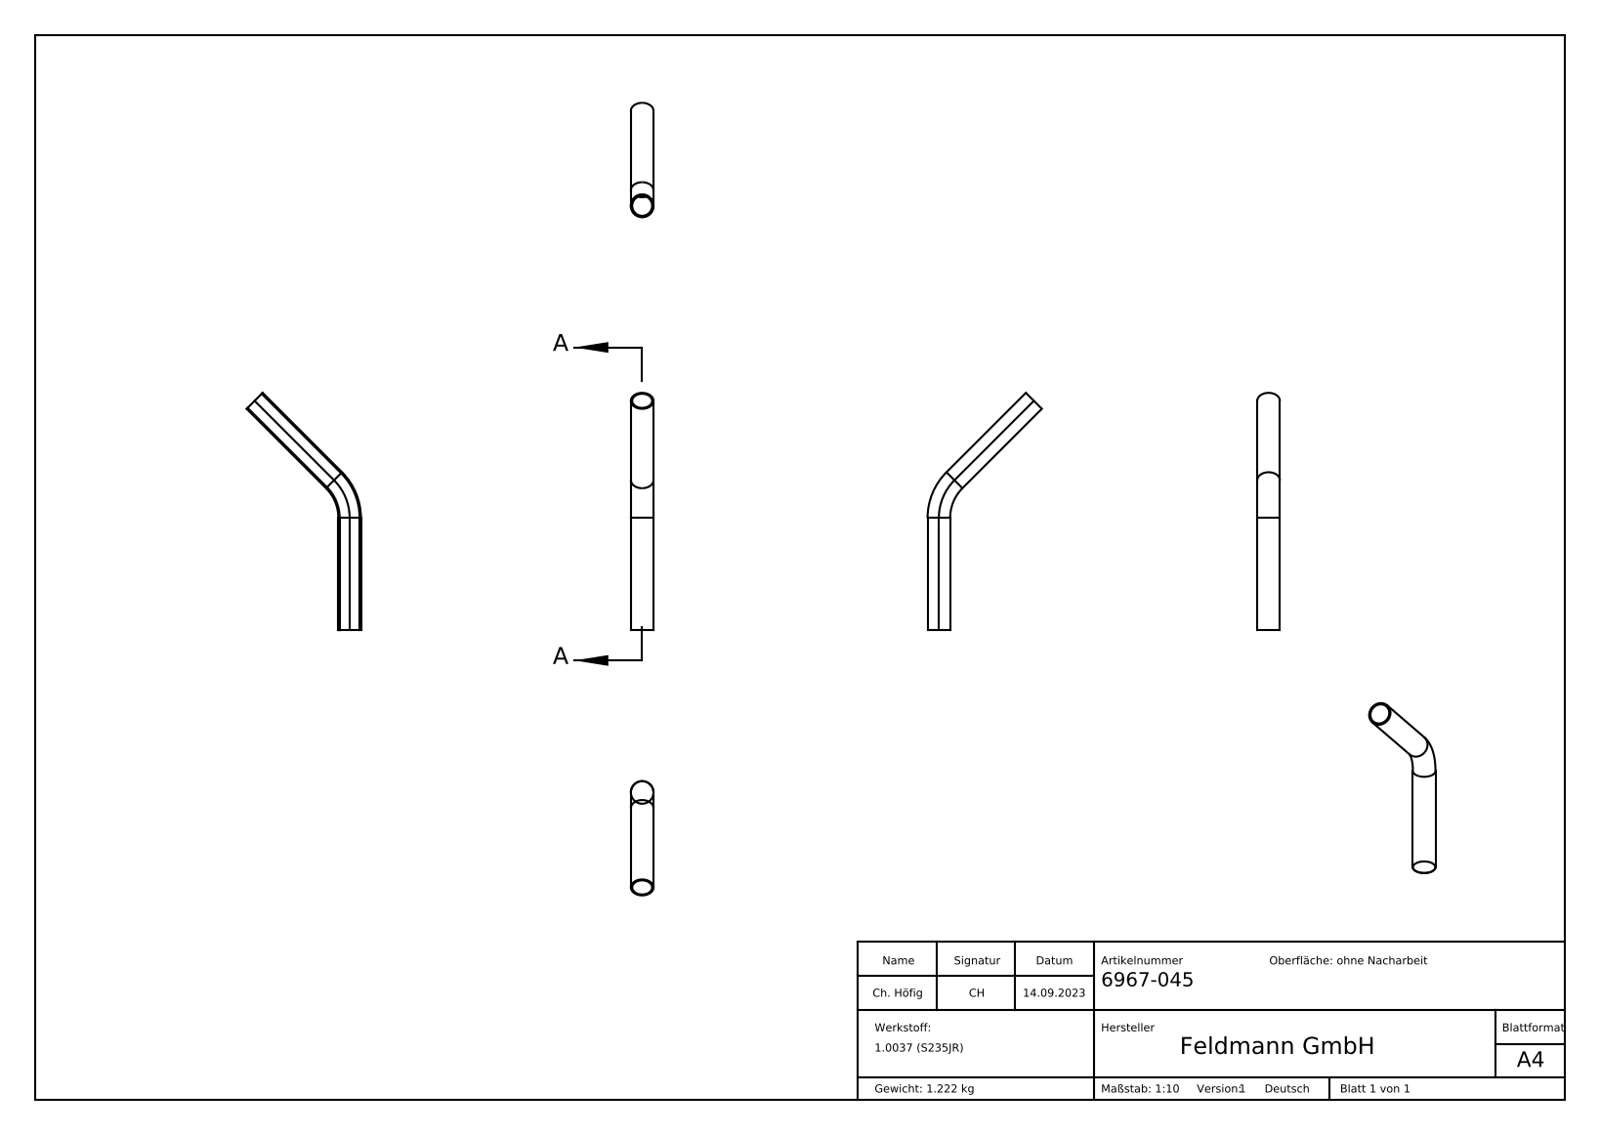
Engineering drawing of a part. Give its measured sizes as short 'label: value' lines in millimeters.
name: 6967-045
written by: SolidWorks 2018 (CONFIG_CONTROL_DESIGN)
unit: mm
bodies: 1 solid, 216 faces (118 planar, 4 cylindrical, 94 other)
size: 445.44 × 214.49 × 42.4
volume: 156 687 mm³; area: 125 980 mm²
holes: 2× ⌀37.4
bosses: 2× ⌀42.4
face distances: 0.54, 0.49, 0.34, 0.53, 0.58, 0.31, 0.39, 0.48, 0.32, 0.42
